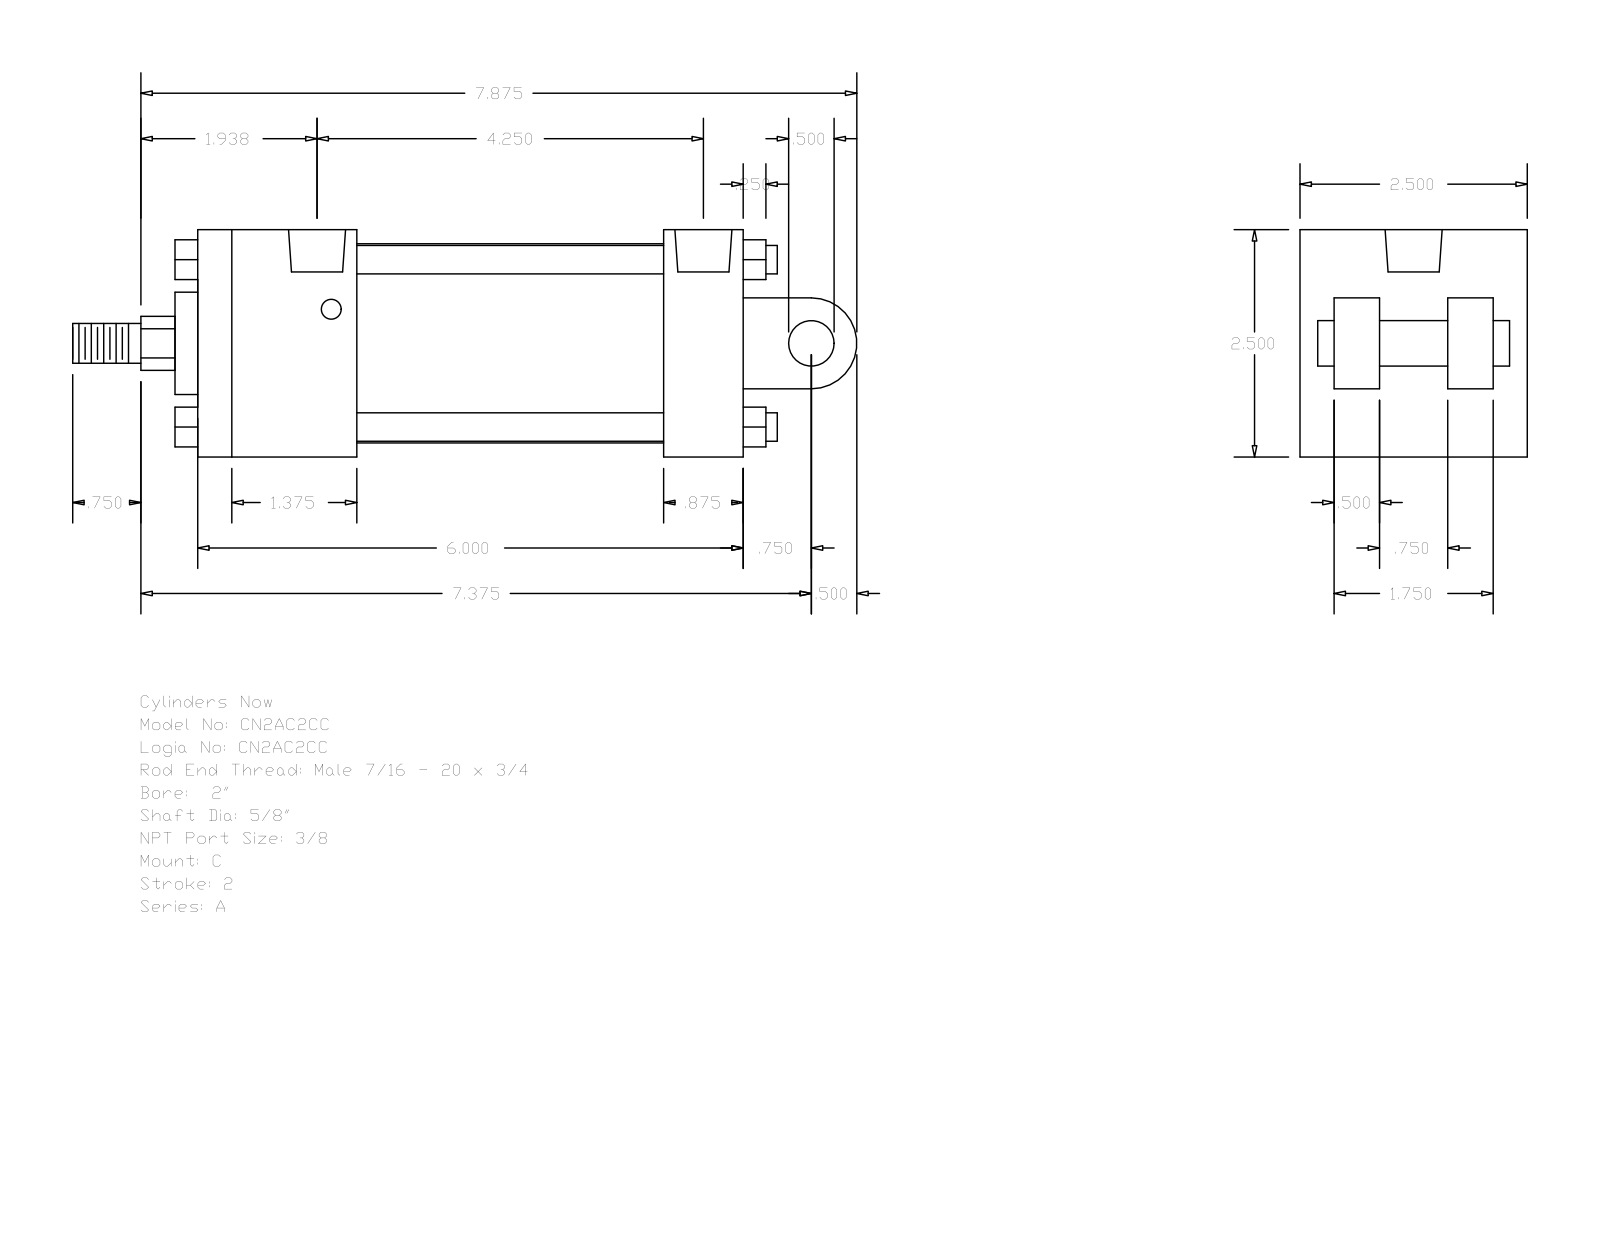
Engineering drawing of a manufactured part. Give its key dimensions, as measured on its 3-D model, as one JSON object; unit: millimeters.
{"part_name": "A_C__0200_0.625", "step_written_by": "GSSL Pune (CONFIG_CONTROL_DESIGN)", "units": "millimeters", "bodies": {"solids": 0, "faces": 135, "planar": 102, "cylindrical": 33, "other": 0}, "overall_size": [219.07, 63.5, 63.5], "round_holes": [[5.56, 4], [15.93, 2]], "round_bosses_or_shafts": [[7.94, 4], [55.63, 1], [28.57, 1], [15.88, 1], [12.7, 1], [11.11, 1]], "partial_cylinders_radius": [[7.54, 1], [12.7, 1]], "face_to_face_distances": [63.5, 152.4, 44.45, 9.52, 107.95, 130.17, 85.72, 22.23, 12.7, 53.98], "hole_center_spacings": [100, 3.97, 3.98, 103.97, 103.98, 107.95]}
